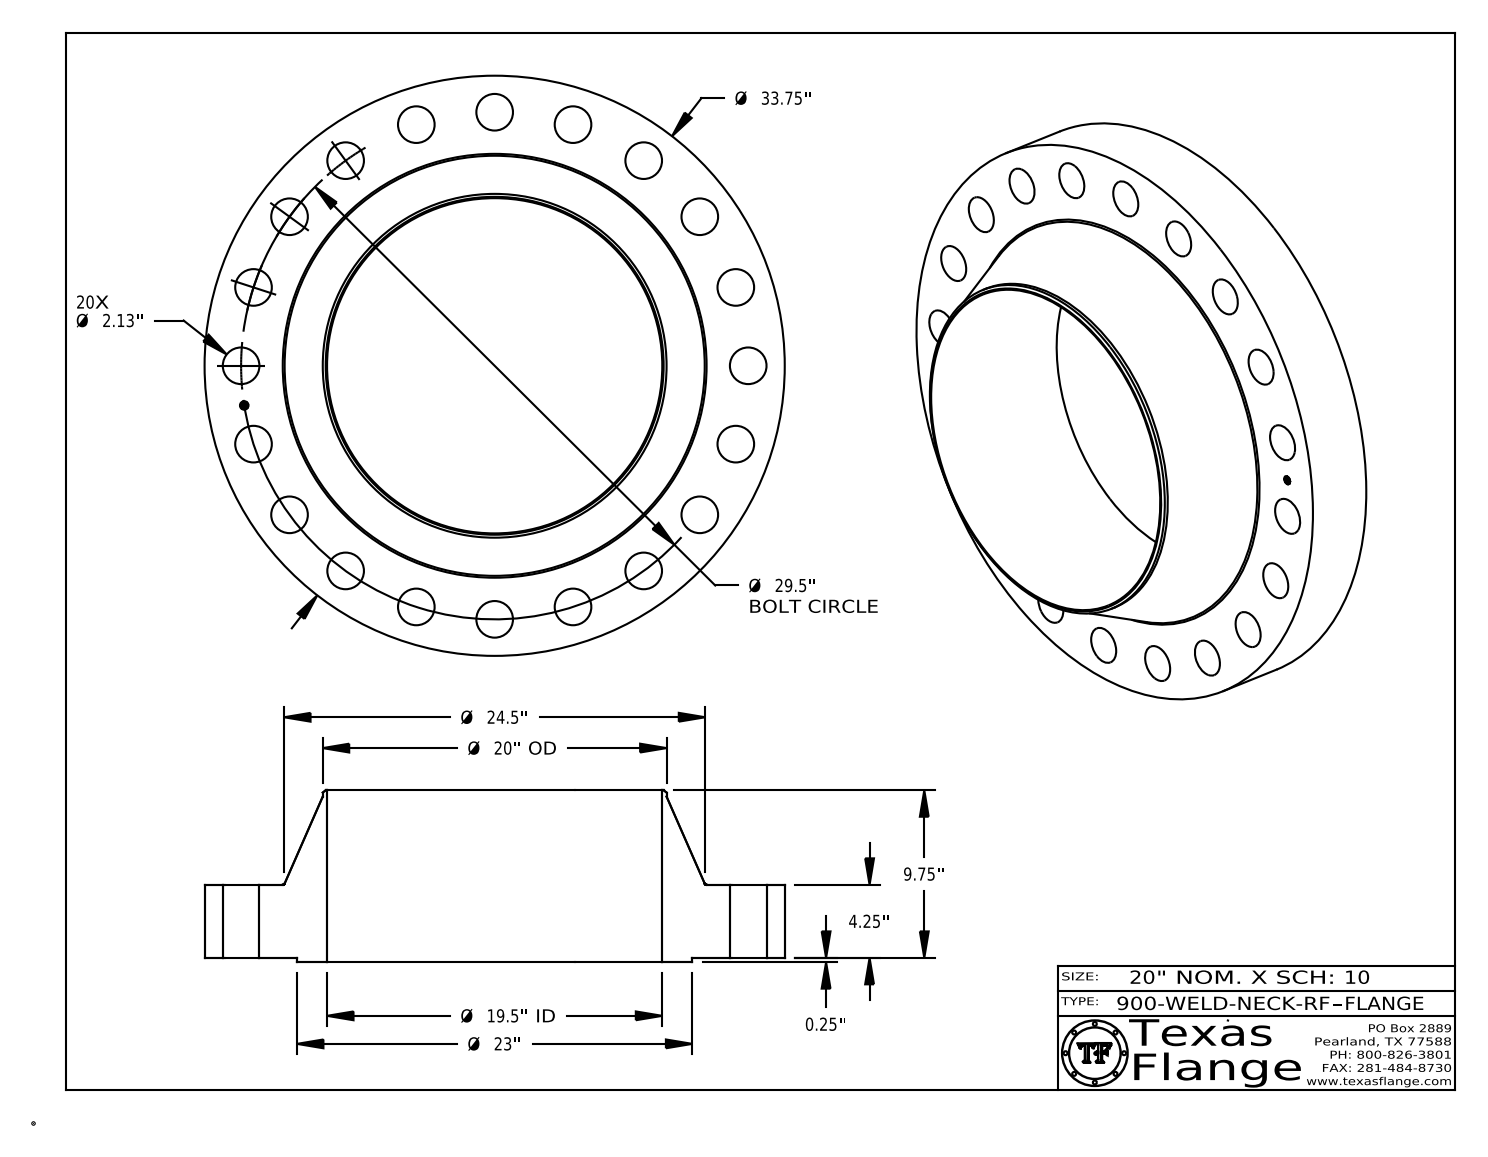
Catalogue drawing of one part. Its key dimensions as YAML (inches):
part_name: "900-WELD-NECK-RF"
step_written_by: "CATIA V5 STEP AP214 (AUTOMOTIVE_DESIGN)"
units: inches
bodies: {solids: 1, faces: 443, planar: 369, cylindrical: 68, other: 6}
overall_size: [33.75, 33.75, 10]
volume: 2734
surface_area: 2950
round_holes:
  - {diameter: 2.13, count: 20}
  - {diameter: 0.495, count: 1}
  - {diameter: 19.5, count: 1}
round_bosses_or_shafts:
  - {diameter: 0.03, count: 8}
  - {diameter: 33.75, count: 1}
  - {diameter: 23, count: 1}
  - {diameter: 20, count: 1}
  - {diameter: 0.39, count: 1}
face_to_face_distances: [4.25, 0.25, 4.5, 10, 9.75, 5.5, 4.485, 4.235, 0.015, 5.515]
hole_center_spacings: [14.75, 29.137, 4.615, 17.34, 20.859, 23.866, 26.285, 9.116]
